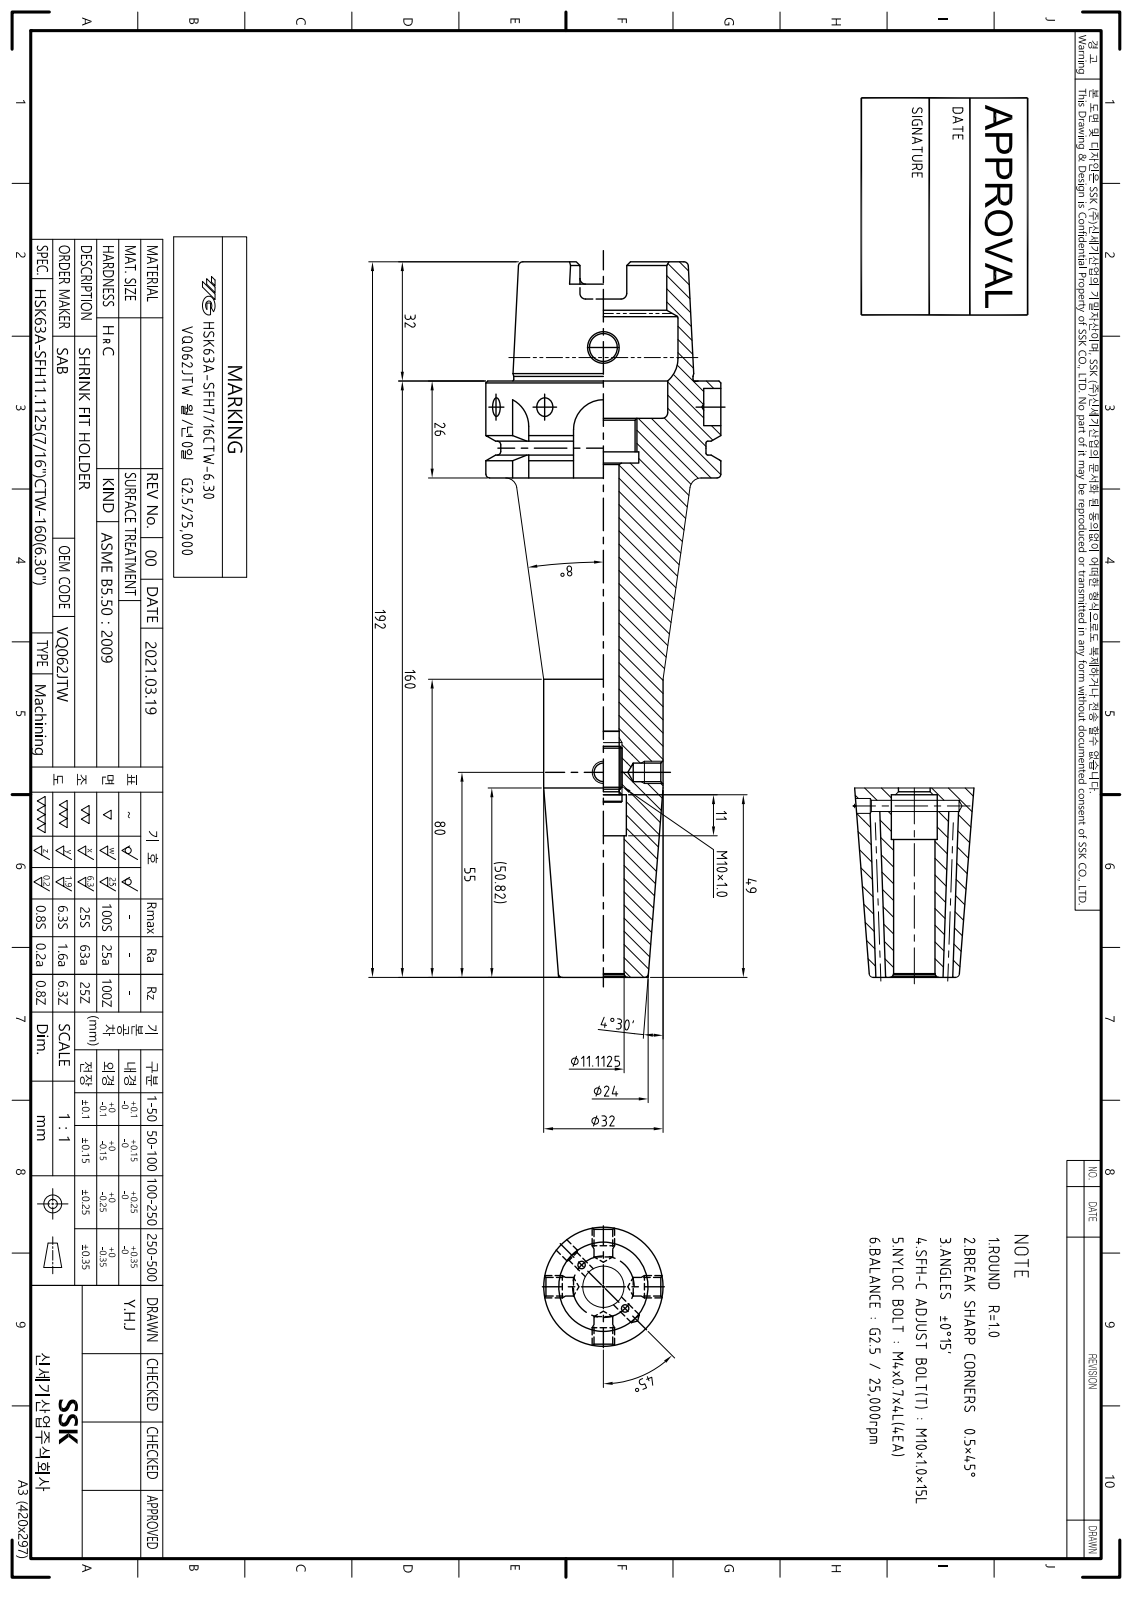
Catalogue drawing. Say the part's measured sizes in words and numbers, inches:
The part is named "LO-HSK63A-SFH11.1125CTW-160". Its 3-D file was written by "Autodesk Inventor 2022 (AUTOMOTIVE_DESIGN)". It is 1 solid with 120 faces: 42 planar, 36 cylindrical and 42 other. Overall it measures 7.559 by 2.48 by 2.48 inches. Its volume is 11.86 cubic inches and its surface area 61.79 square inches. Round holes: 2 of diameter 0.079, 1 of diameter 0.169, 1 of diameter 0.295, 1 of diameter 0.315, 1 of diameter 0.394, 1 of diameter 0.437, 1 of diameter 0.485, 1 of diameter 0.666, 1 of diameter 0.748, 1 of diameter 1.339, 1 of diameter 1.575. Round bosses or shafts: 1 of diameter 2.48, 1 of diameter 2.165, 1 of diameter 1.891, 1 of diameter 1.26. Partial cylindrical surfaces (rounded edges, fillets, slot ends): 6 of radius 0.059, 4 of radius 0.113, 4 of radius 0.315. The main face-to-face distances are 1.024, 0.394, 0.63, 1.26, 1.654, 2.283, 7.559, 6.299, 5.906, 5.276.
